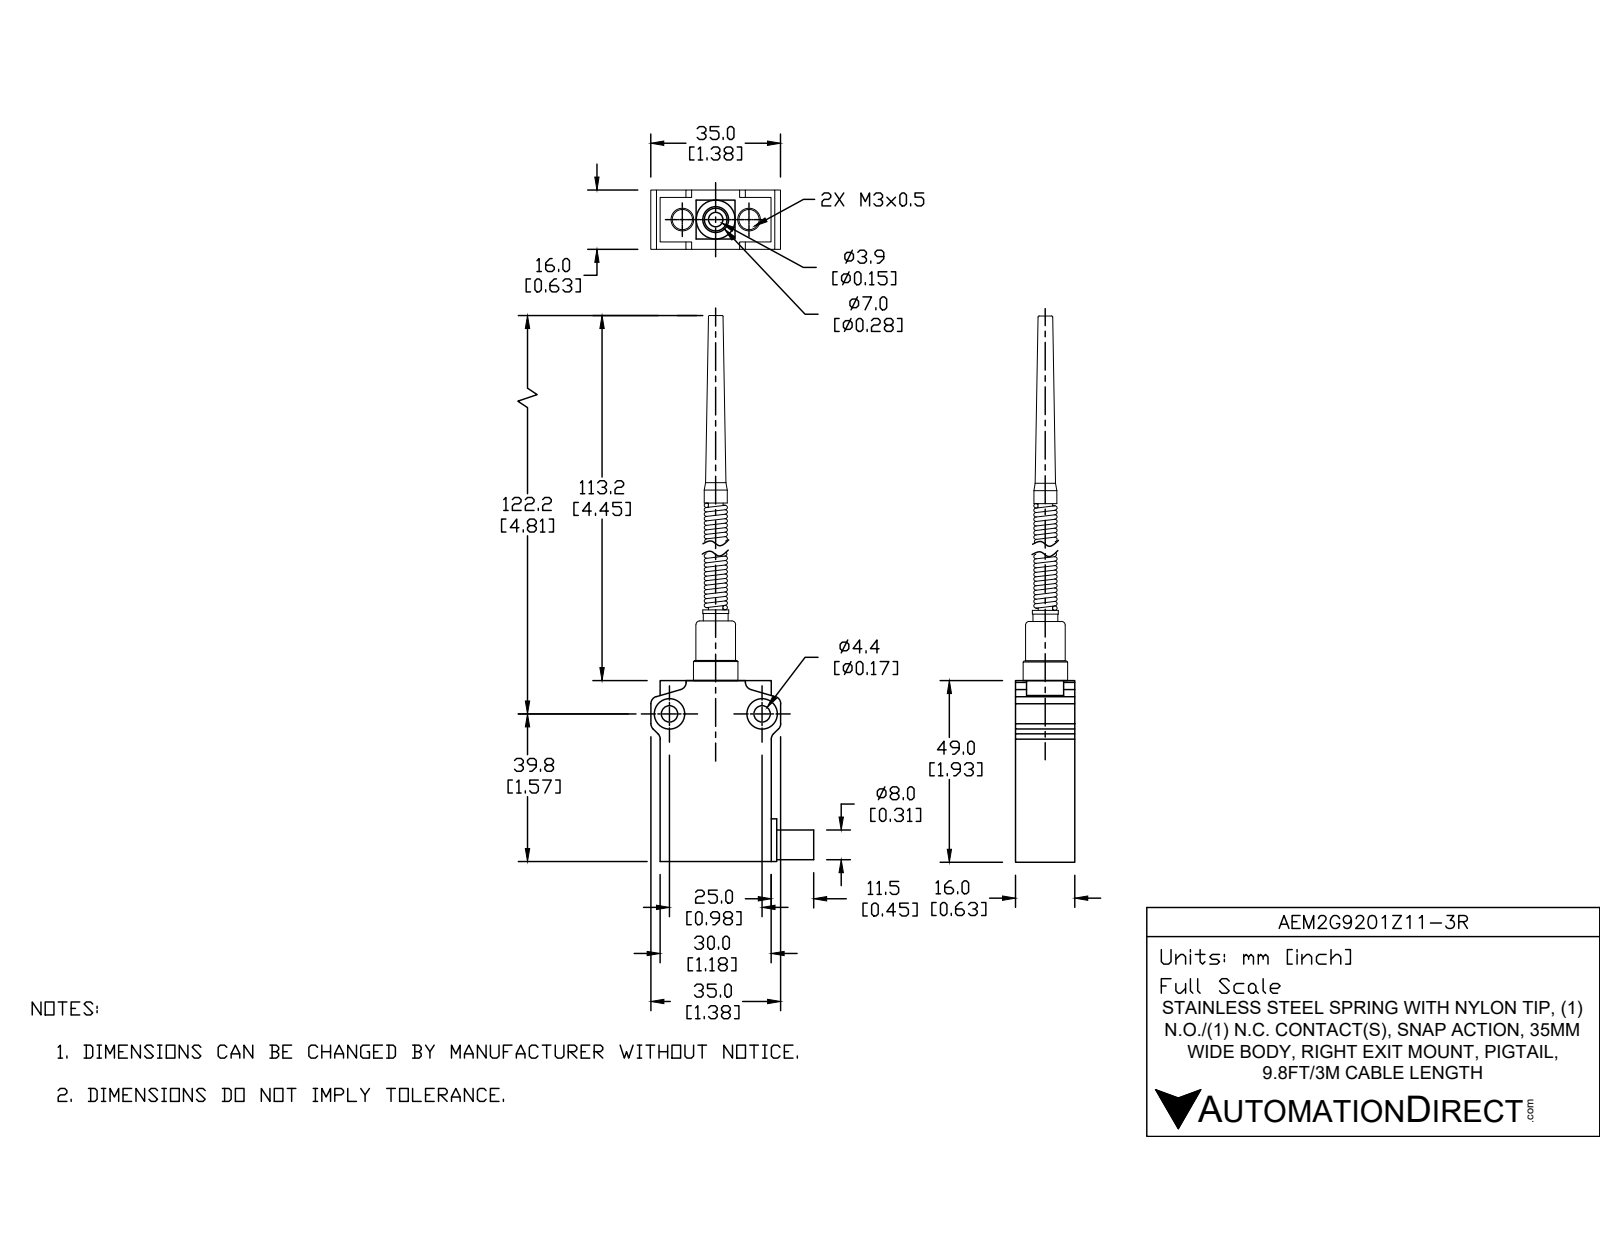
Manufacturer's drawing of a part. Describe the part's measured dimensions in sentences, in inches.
The part is named "AEM2G9201Z11-3R". Its 3-D file was written by "SolidWorks 2017 (AUTOMOTIVE_DESIGN)". It is 5 solids with 114 faces: 51 planar, 46 cylindrical and 17 other. Overall it measures 6.307 by 1.87 by 0.63 inches. Its volume is 1.628 cubic inches and its surface area 17.32 square inches. Round holes: 2 of diameter 0.118, 2 of diameter 0.173, 2 of diameter 0.323, 1 of diameter 0.512. Round bosses or shafts: 1 of diameter 0.472, 1 of diameter 0.433, 1 of diameter 0.323, 1 of diameter 0.276, 1 of diameter 0.268. Partial cylindrical surfaces (rounded edges, fillets, slot ends): 8 of radius 0.079. The main face-to-face distances are 0.63, 1.181, 1.929, 1.74, 0.189, 0.472, 0.098, 1.28, 0.157, 1.772. The hole center spacings are 0.374, 0.748, 0.984.
